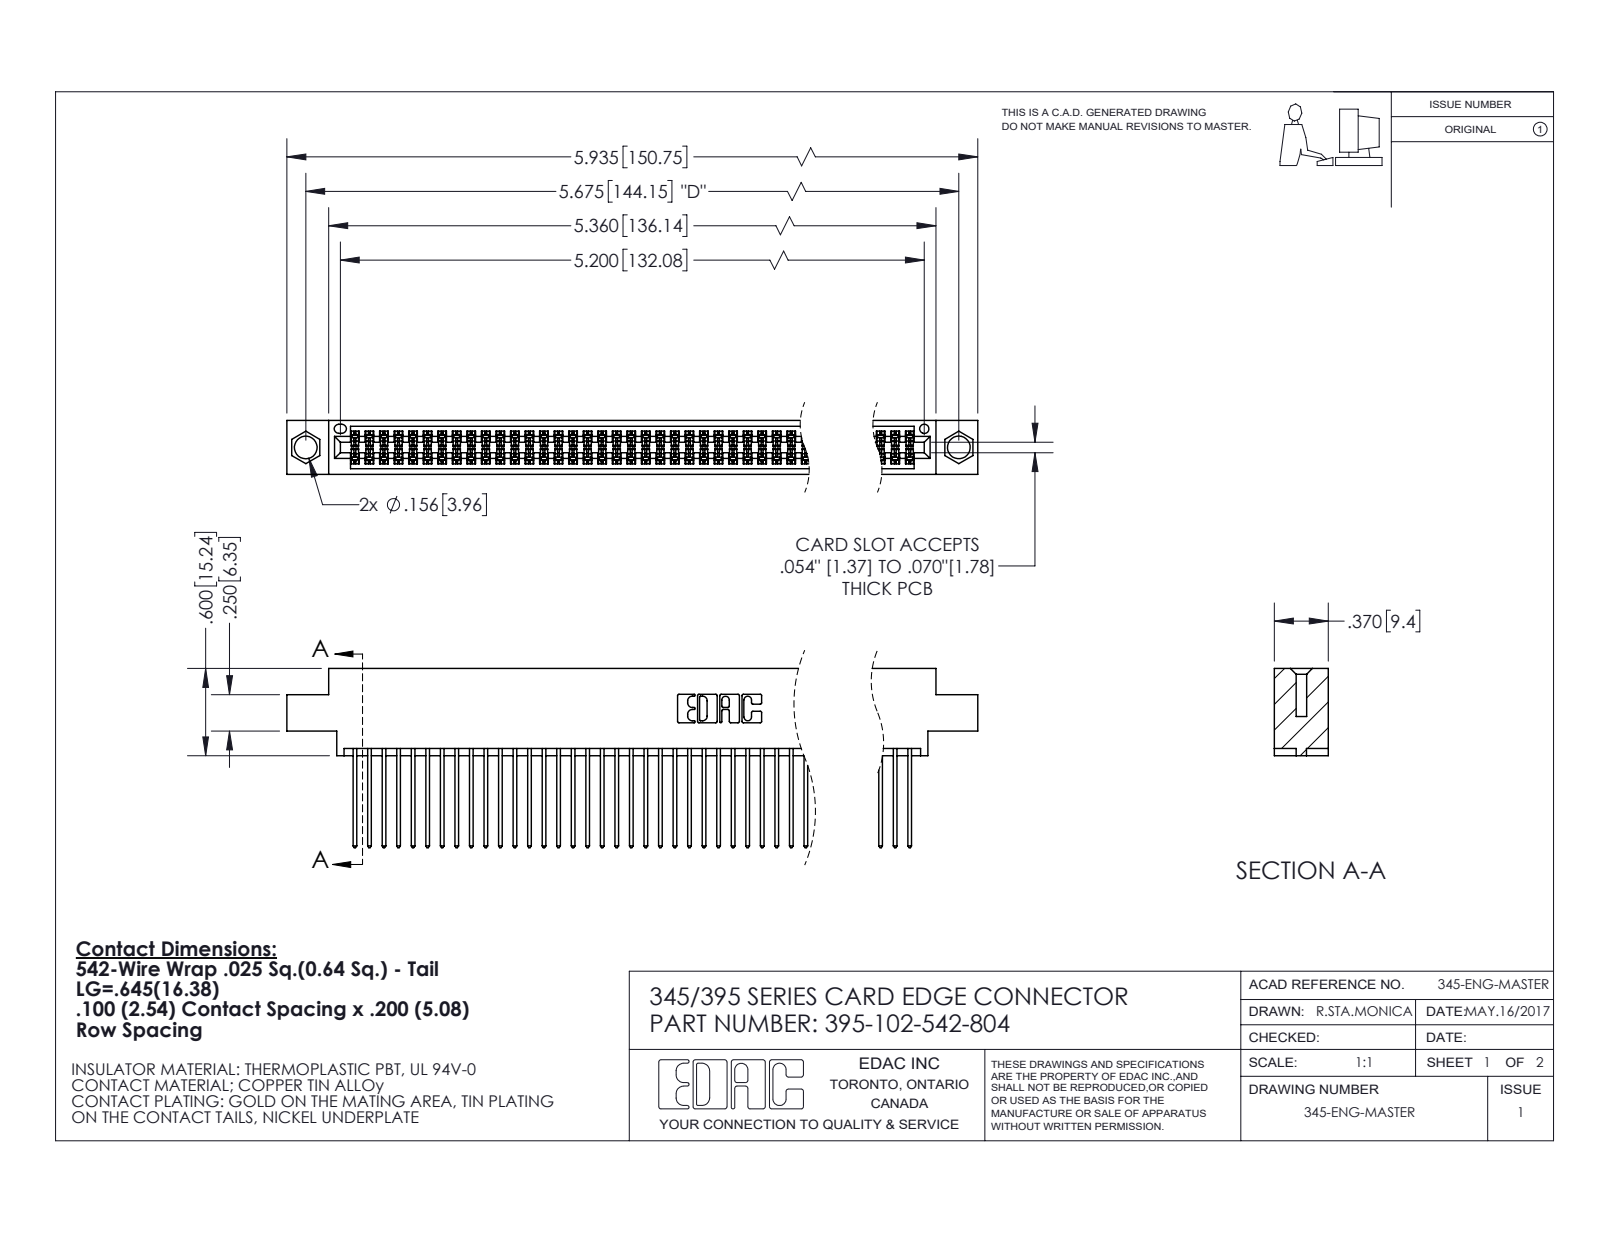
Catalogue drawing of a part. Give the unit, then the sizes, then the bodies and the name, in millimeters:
Units: millimetres
Overall size (bounding box): 150.7 × 31.3 × 9.4
Round holes (diameter × count): ⌀4 ×2, ⌀1.6 ×1
Partial cylindrical surfaces — rounded edges, fillets, slot ends (radius × count): R0.2 ×153, R0.3 ×102, R0.3 ×22, R0.2 ×6, R0.8 ×6, R0.7 ×3, R0.4 ×2, R0.5 ×2
Main face-to-face distances: 1.8, 7.6, 5.1, 2.5, 6.9, 0.6, 9.4, 5.7, 4.4, 3.8
Hole centre spacings: 6.9, 138.2, 144.1
Volume: 15 000 mm³ · Surface area: 24 540 mm²
Bodies: 103 solids, 5244 faces (3464 planar, 1780 cylindrical, 0 other)
Part name (STEP PRODUCT): 345 Part_0.170 Offset - 0.156 Dia-TI; 395-102-542-804; 345-292-001_345-293-142
STEP written by: SolidWorks 2020 (CONFIG_CONTROL_DESIGN)
